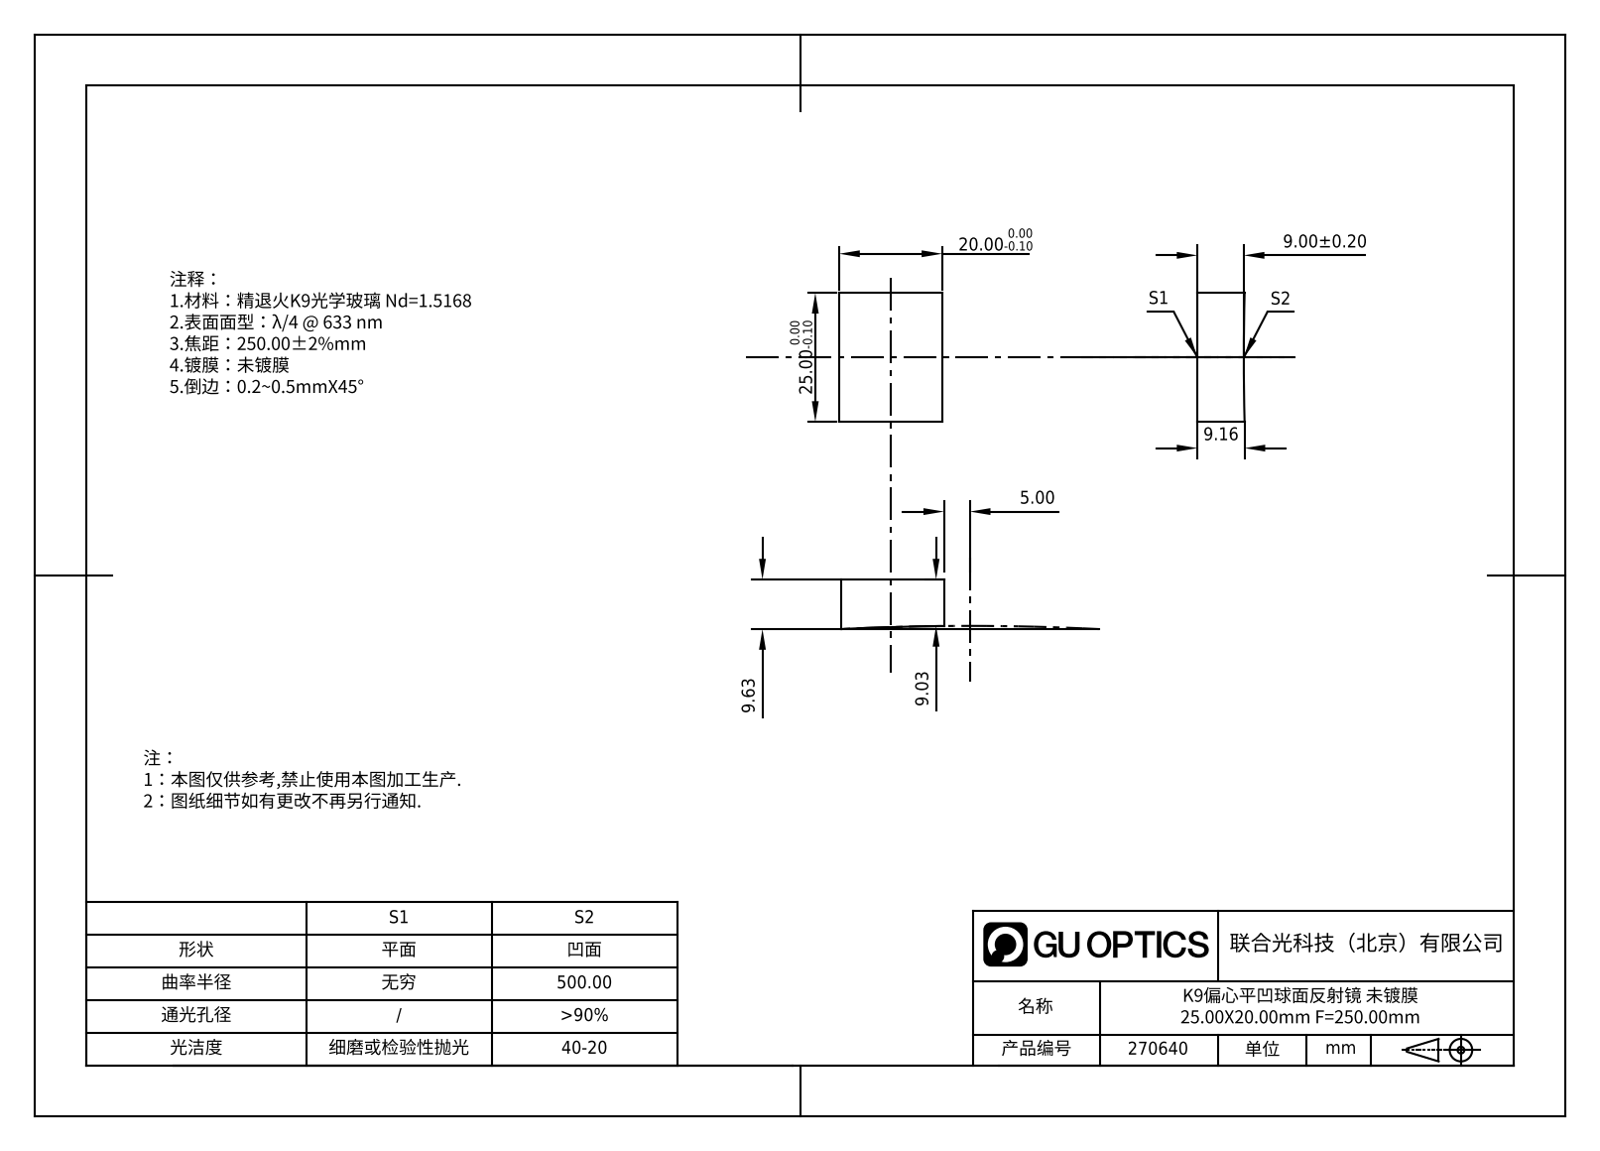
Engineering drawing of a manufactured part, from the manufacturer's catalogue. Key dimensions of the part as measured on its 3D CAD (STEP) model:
Part name (STEP PRODUCT): 270640
STEP written by: SolidWorks 2020 (CONFIG_CONTROL_DESIGN)
Units: millimetres
Bodies: 1 solid, 7 faces (5 planar, 0 cylindrical, 2 other)
Overall size (bounding box): 25 × 20 × 9.78
Volume: 4 655 mm³ · Surface area: 1 846 mm²
Main face-to-face distances: 20, 25
